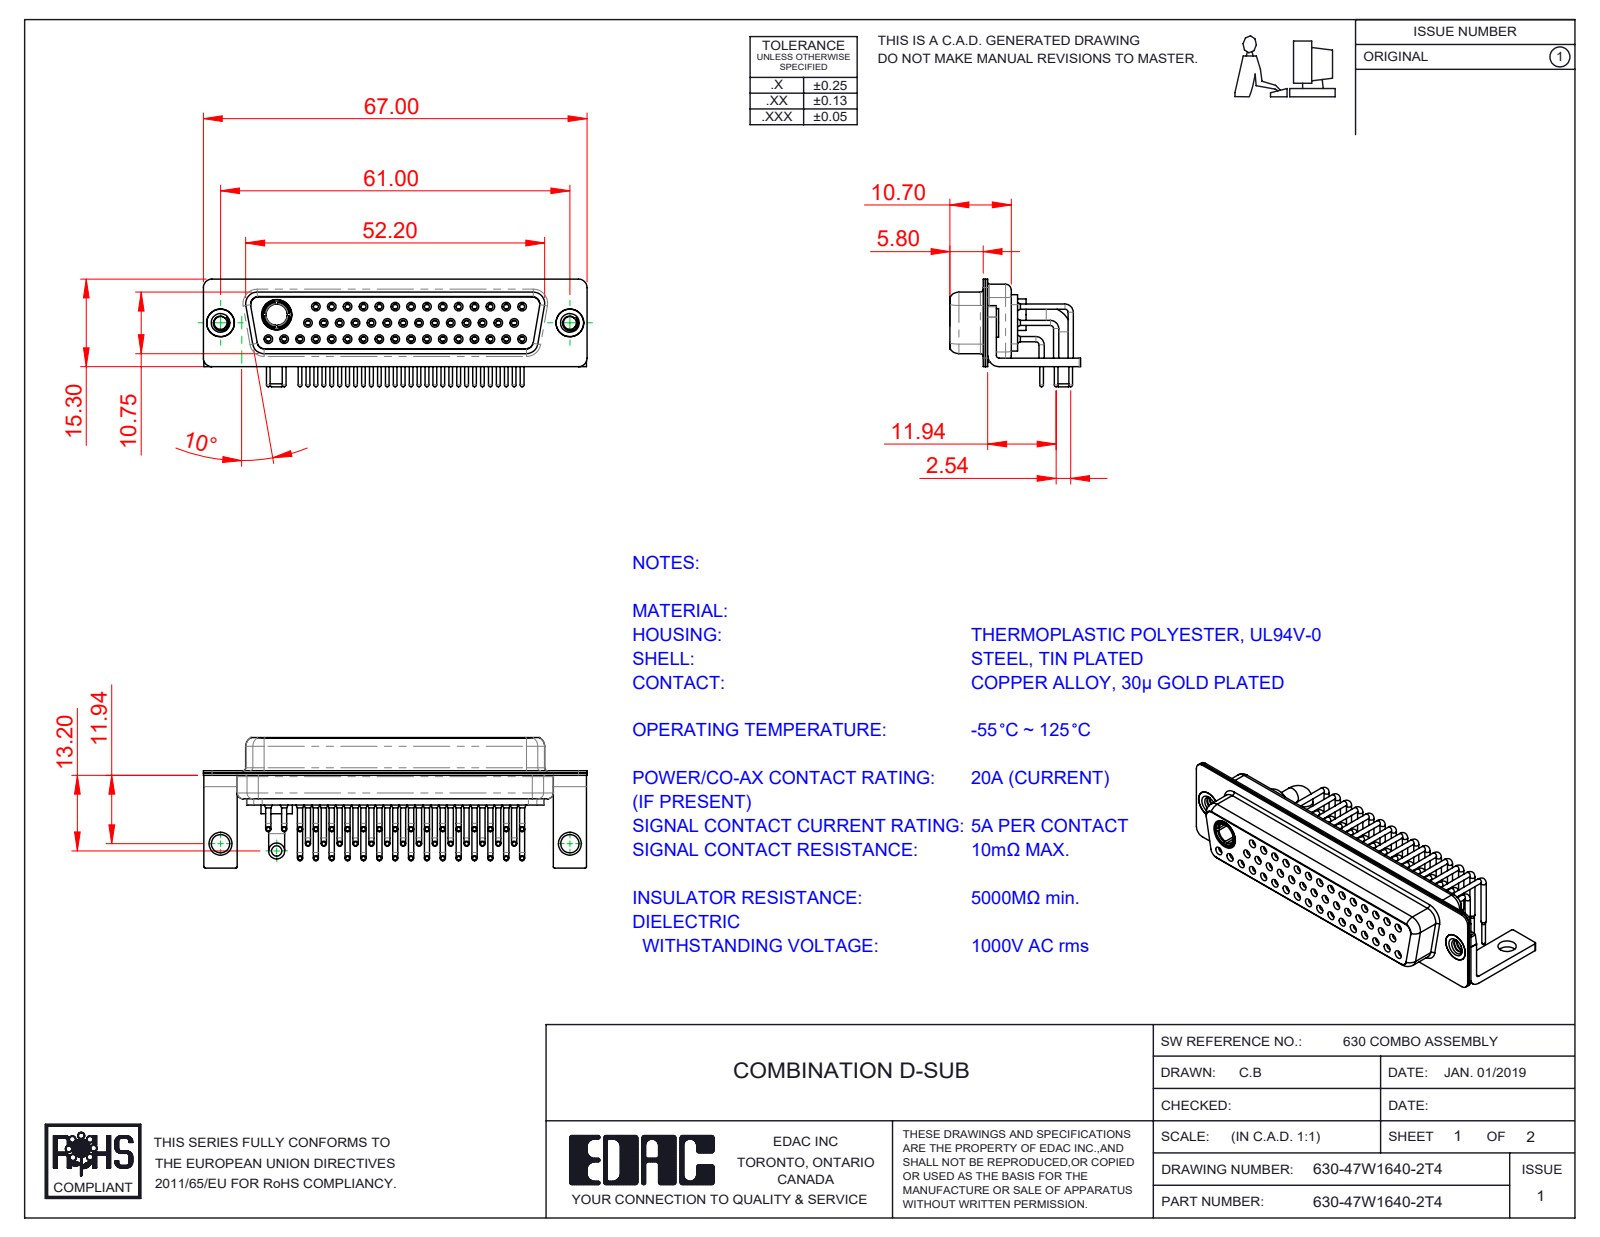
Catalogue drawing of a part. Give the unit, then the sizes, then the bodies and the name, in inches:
Units: inches
Overall size (bounding box): 2.638 × 0.898 × 0.74
Round holes (diameter × count): ⌀0.043 ×46, ⌀0.035 ×45, ⌀0.059 ×45, ⌀0.079 ×45, ⌀0.063 ×31, ⌀0.067 ×14, ⌀0.191 ×3, ⌀0.089 ×2, ⌀0.126 ×2, ⌀0.157 ×2, ⌀0.159 ×2, ⌀0.146 ×1
Round bosses / shafts (diameter × count): ⌀0.035 ×48, ⌀0.026 ×46, ⌀0.063 ×16, ⌀0.197 ×2, ⌀0.195 ×2, ⌀0.189 ×2, ⌀0.11 ×2, ⌀0.079 ×2
Partial cylindrical surfaces — rounded edges, fillets, slot ends (radius × count): R0.01 ×16, R0.059 ×16, R0.079 ×13, R0.053 ×12, R0.063 ×8, R0.02 ×5, R0.024 ×4, R0.026 ×4
Main face-to-face distances: 0.016, 0.236, 0.22, 0.031, 0.059, 0.228, 0.205, 0.444, 0.072, 0.465
Hole centre spacings: 0.124, 0.109, 0.218, 0.327, 0.436, 0.545, 0.654, 0.763
Volume: 0.463 in³ · Surface area: 25.93 in²
Bodies: 55 solids, 2822 faces (803 planar, 1230 cylindrical, 789 other)
Part name (STEP PRODUCT): 630Combo Housing_47W1; 630Combo Shell Rear_50 Contacts; 630Combo Threaded Rivet_3; Power Socket_20A RA 50 (+6 more)
STEP written by: SolidWorks 2020 (CONFIG_CONTROL_DESIGN)
